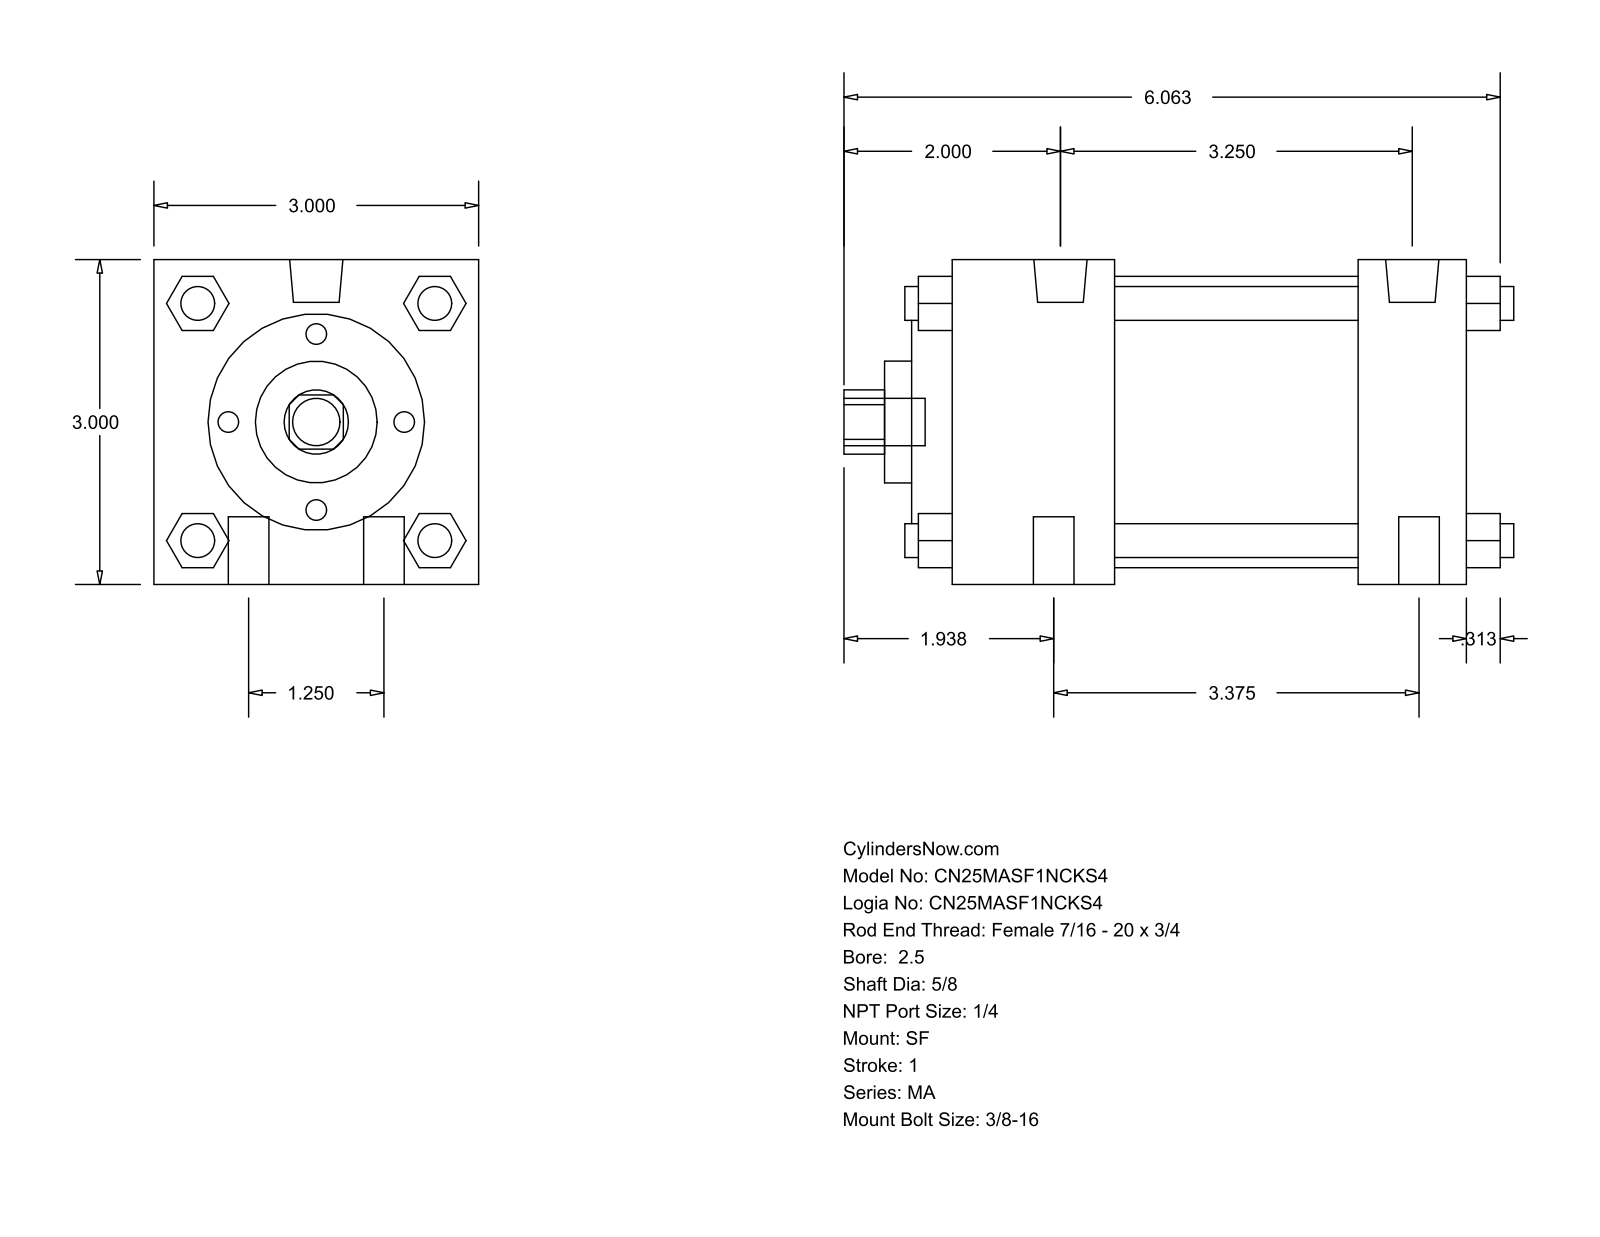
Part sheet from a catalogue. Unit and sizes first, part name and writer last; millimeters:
Units: millimetres
Overall size (bounding box): 157.16 × 76.2 × 76.2
Round holes (diameter × count): ⌀15.88 ×1, ⌀28.57 ×1, ⌀50.8 ×1, ⌀68.33 ×1
Round bosses / shafts (diameter × count): ⌀7.94 ×6, ⌀9.53 ×4, ⌀12.49 ×2, ⌀11.11 ×1
Partial cylindrical surfaces — rounded edges, fillets, slot ends (radius × count): R7.54 ×1
Main face-to-face distances: 76.2, 120.65, 25.4, 57.15, 95.25, 38.1, 82.55, 12.7, 9.52, 47.62
Bodies: 0 solids, 126 faces (95 planar, 31 cylindrical, 0 other)
Part name (STEP PRODUCT): MA_SF__0250_0.625
STEP written by: GSSL Pune (CONFIG_CONTROL_DESIGN)
